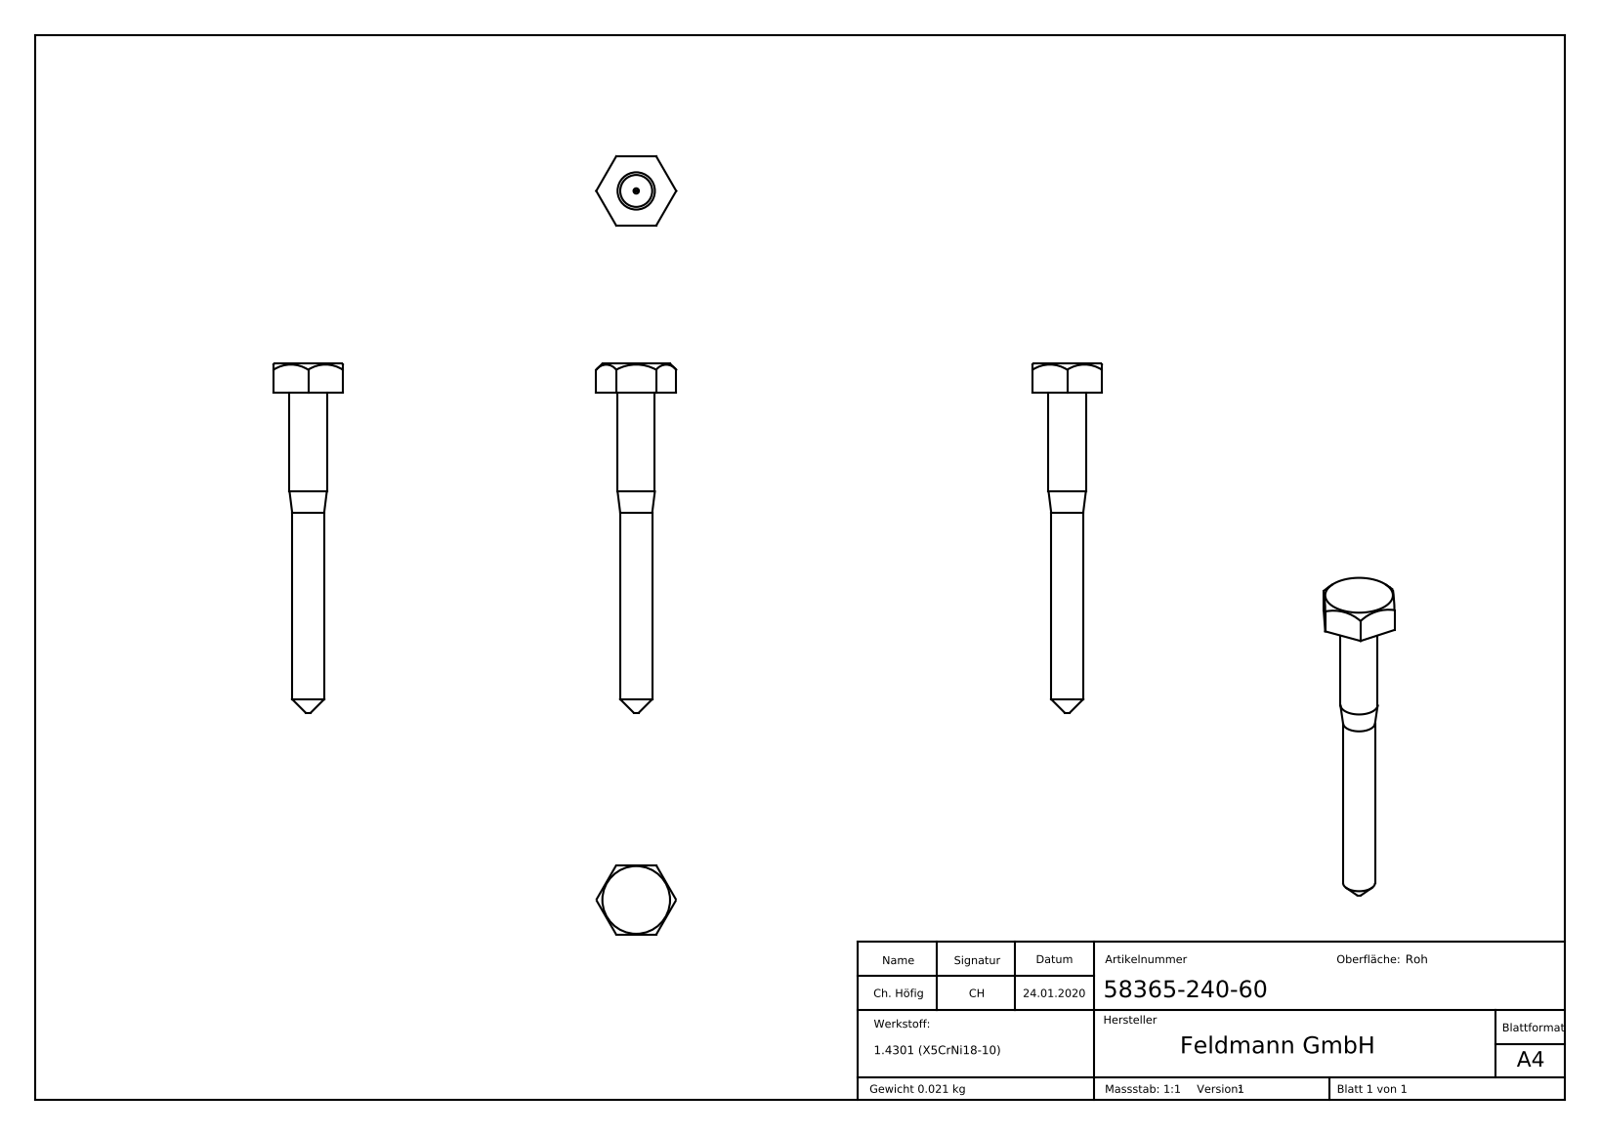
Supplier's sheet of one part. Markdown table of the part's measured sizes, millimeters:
| quantity | value |
| --- | --- |
| part name | 58365-240-60 |
| STEP written by | SolidWorks 2015 (CONFIG_CONTROL_DESIGN) |
| units | millimeters |
| bodies | 1 solid, 283 faces (141 planar, 2 cylindrical, 140 other) |
| overall size | 65.5 × 15.01 × 13 |
| volume | 2 661 mm³ |
| surface area | 1 677 mm² |
| round bosses / shafts (diameter × count) | 7 × 1, 6 × 1 |
| main face-to-face distances | 13, 5.5, 60, 65.5, 6.52, 6.48, 6.5, 59.9, 65.4, 6.54 |
